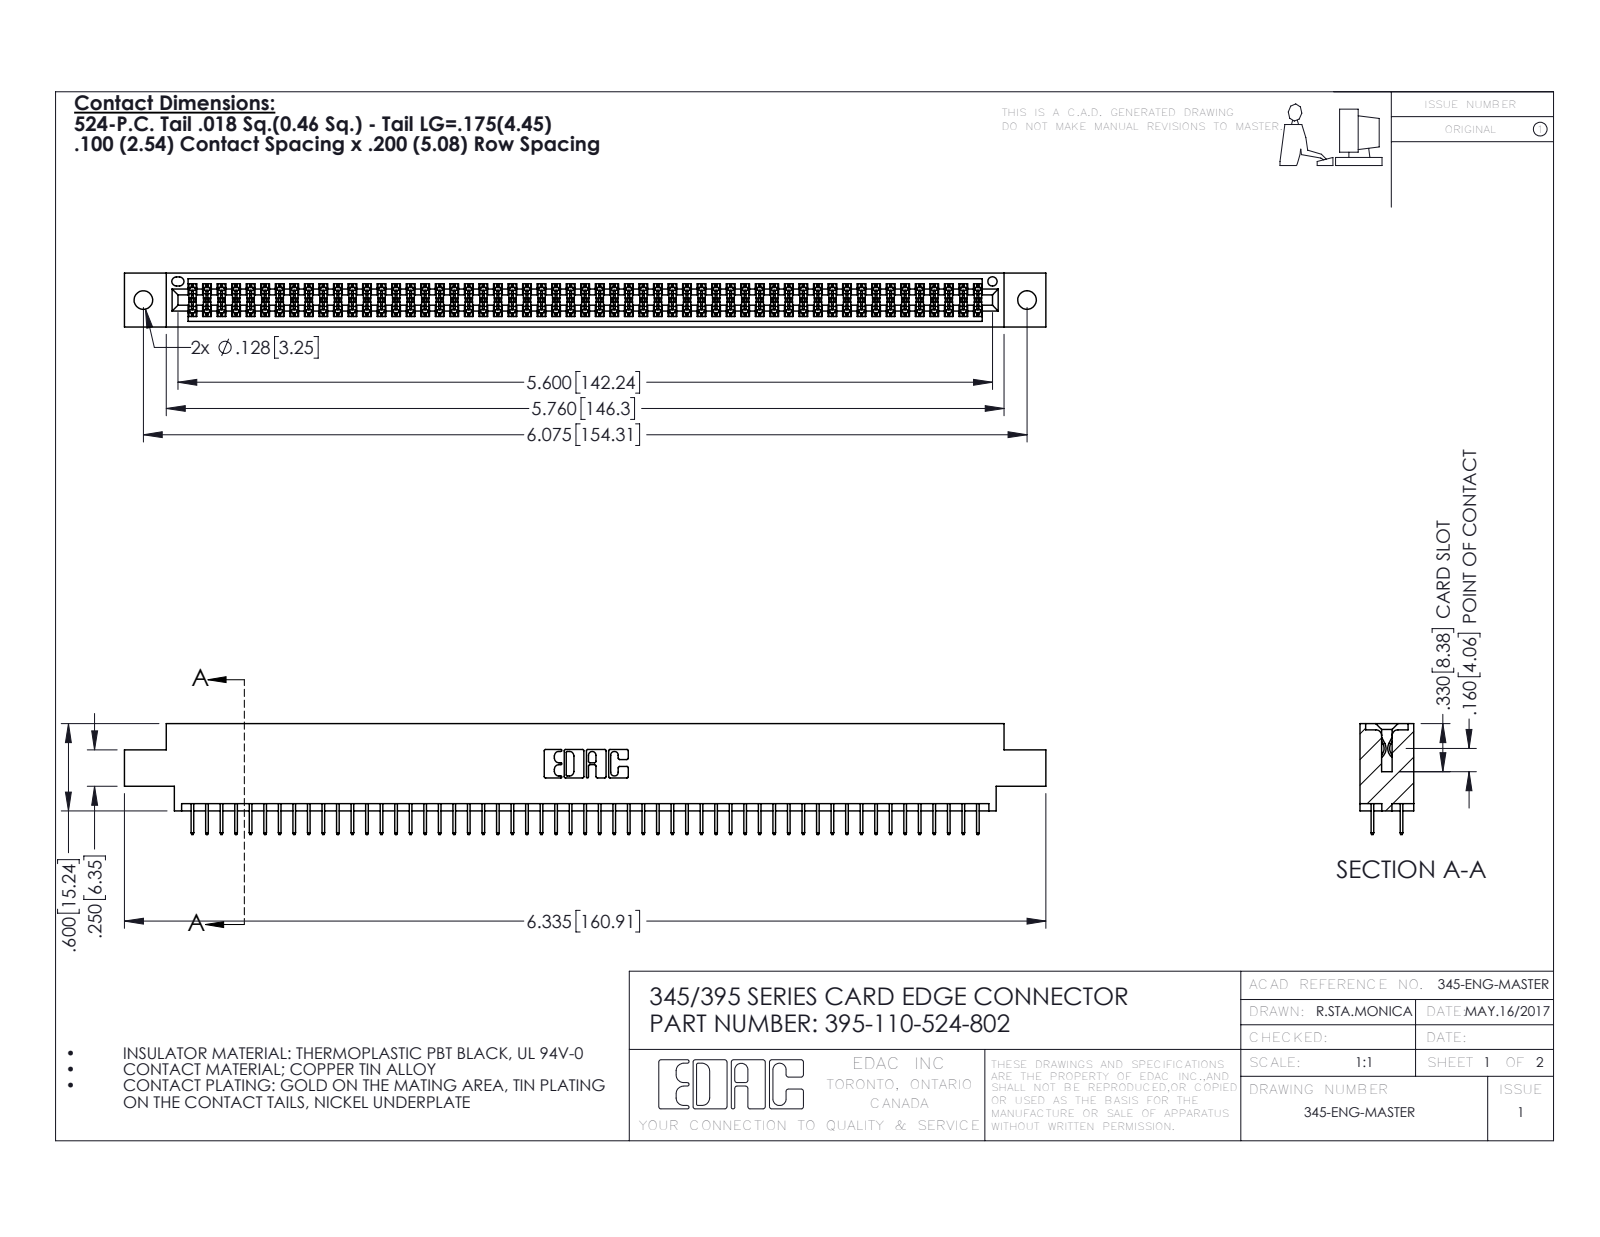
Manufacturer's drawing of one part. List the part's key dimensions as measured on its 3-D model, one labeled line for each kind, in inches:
Part name (STEP PRODUCT): 345-292-001_345-293-124; 345 Part_0.170 Offset - 0.128 Dia; 395-110-524-802
STEP written by: SolidWorks 2016 (CONFIG_CONTROL_DESIGN)
Units: inches
Bodies: 111 solids, 6070 faces (4374 planar, 1696 cylindrical, 0 other)
Overall size (bounding box): 6.335 × 0.762 × 0.37
Volume: 0.942 in³ · Surface area: 34.87 in²
Round holes (diameter × count): ⌀0.128 ×2, ⌀0.064 ×1
Partial cylindrical surfaces — rounded edges, fillets, slot ends (radius × count): R0.006 ×165, R0.01 ×22, R0.007 ×6, R0.031 ×6, R0.026 ×3, R0.014 ×2, R0.019 ×2, R0.022 ×2
Main face-to-face distances: 0.072, 0.298, 0.37, 0.2, 0.098, 0.272, 0.025, 0.225, 0.072, 0.175
Hole centre spacings: 0.27, 5.839, 6.075
